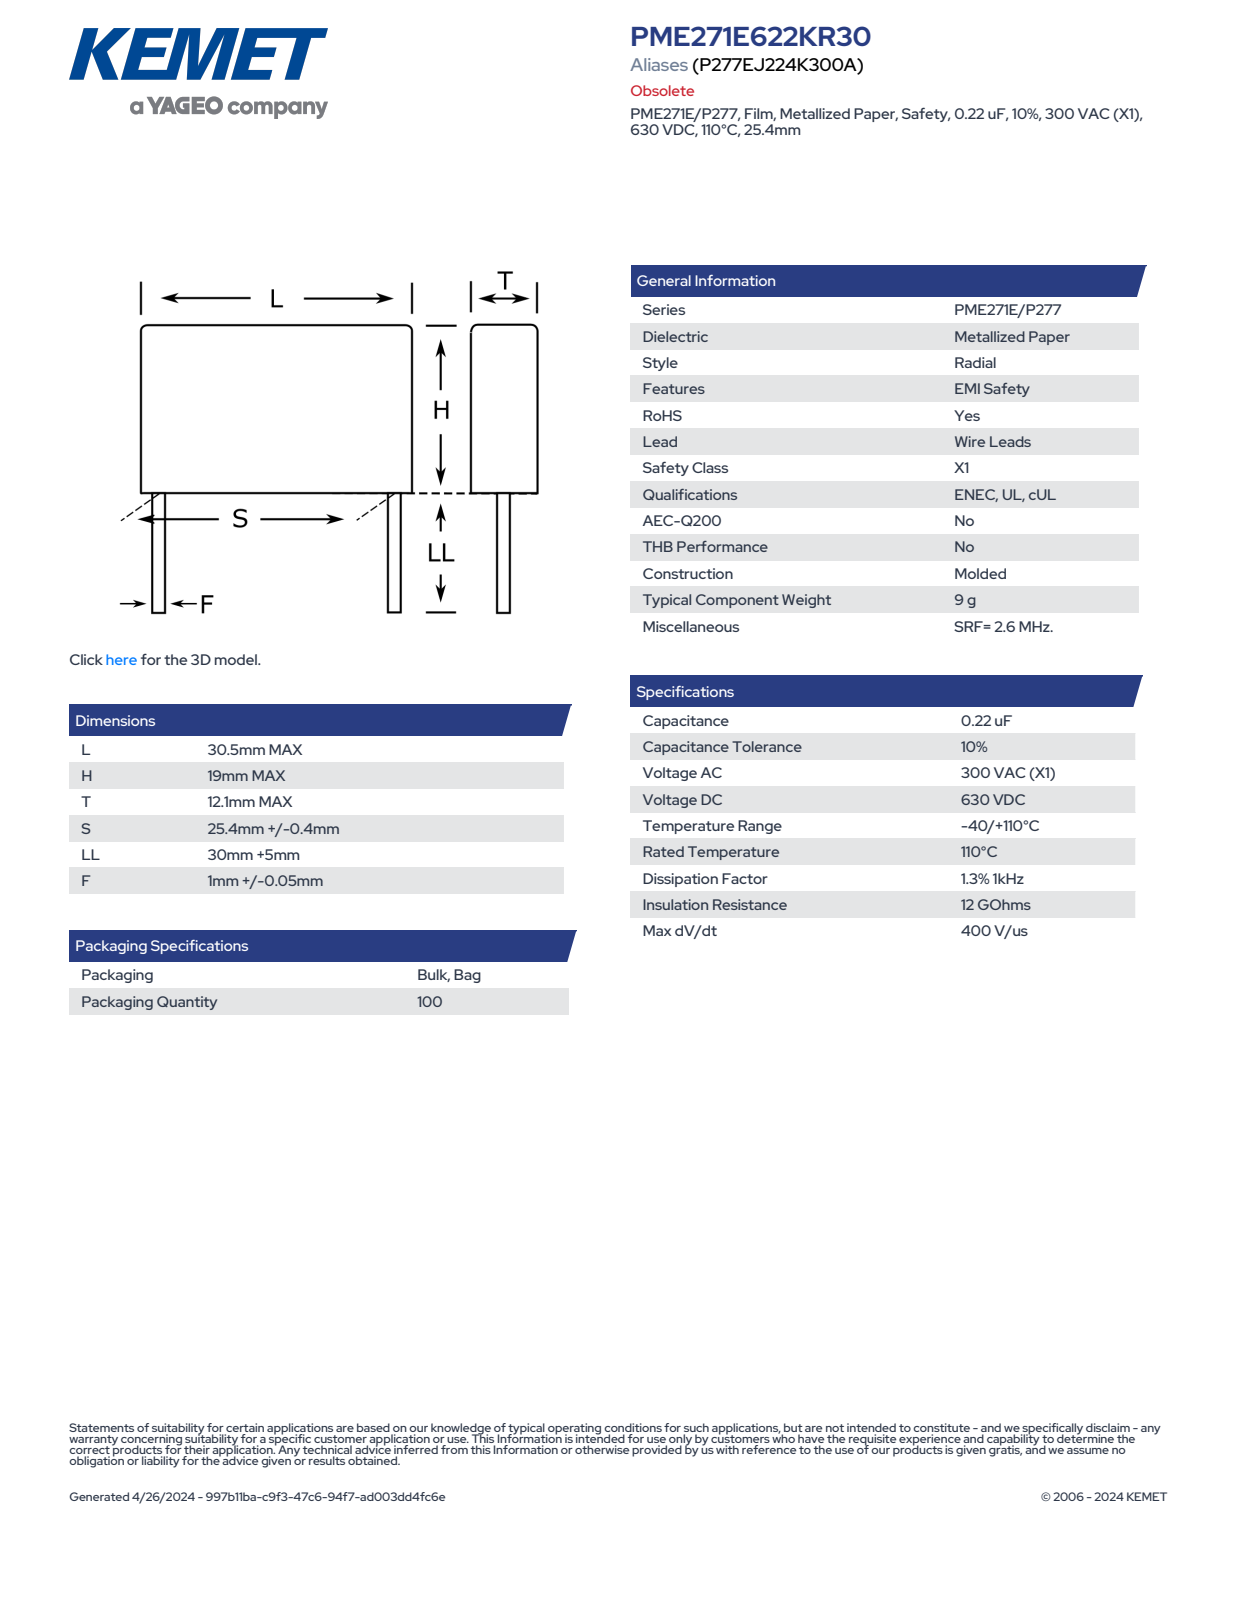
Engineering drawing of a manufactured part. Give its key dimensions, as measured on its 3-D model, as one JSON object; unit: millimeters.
{"part_name": "CFR_MOLDED_30.5X19X12.1_L30.5H19T12.1S25.4LL35F1.05", "step_written_by": "SolidWorks 2014 (AUTOMOTIVE_DESIGN)", "units": "millimeters", "bodies": {"solids": 4, "faces": 73, "planar": 65, "cylindrical": 8, "other": 0}, "overall_size": [54, 30.5, 12.11], "volume_mm3": 7068, "surface_area_mm2": 2614, "round_bosses_or_shafts": [[1.05, 2]], "partial_cylinders_radius": [[0.5, 4]], "face_to_face_distances": [12.1, 19, 30.5, 35, 54, 45.7, 10.7, 8.3, 42.97, 7.97]}
